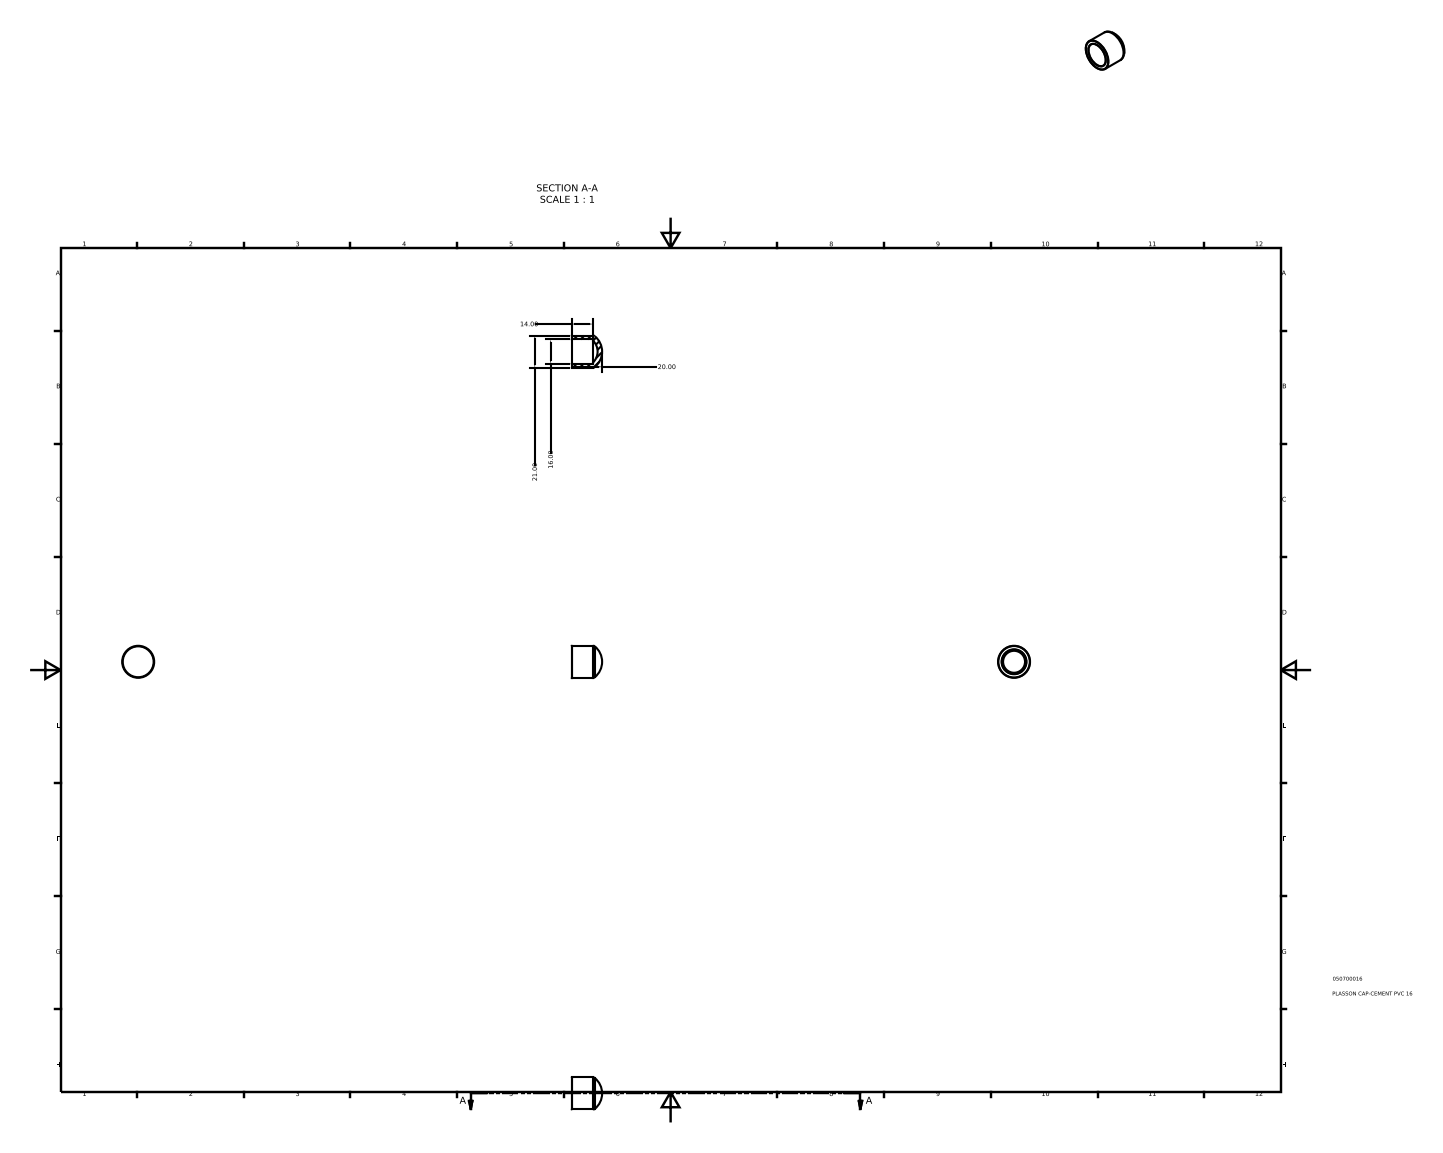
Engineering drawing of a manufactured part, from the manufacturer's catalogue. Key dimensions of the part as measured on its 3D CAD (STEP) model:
Part name (STEP PRODUCT): 050700016
STEP written by: Autodesk Inventor 2015 (AUTOMOTIVE_DESIGN)
Units: millimetres
Bodies: 1 solid, 9 faces (2 planar, 2 cylindrical, 5 other)
Overall size (bounding box): 21 × 21 × 20
Volume: 3 009 mm³ · Surface area: 2 472 mm²
Round holes (diameter × count): ⌀16 ×1
Round bosses / shafts (diameter × count): ⌀21 ×1
Main face-to-face distances: 14
